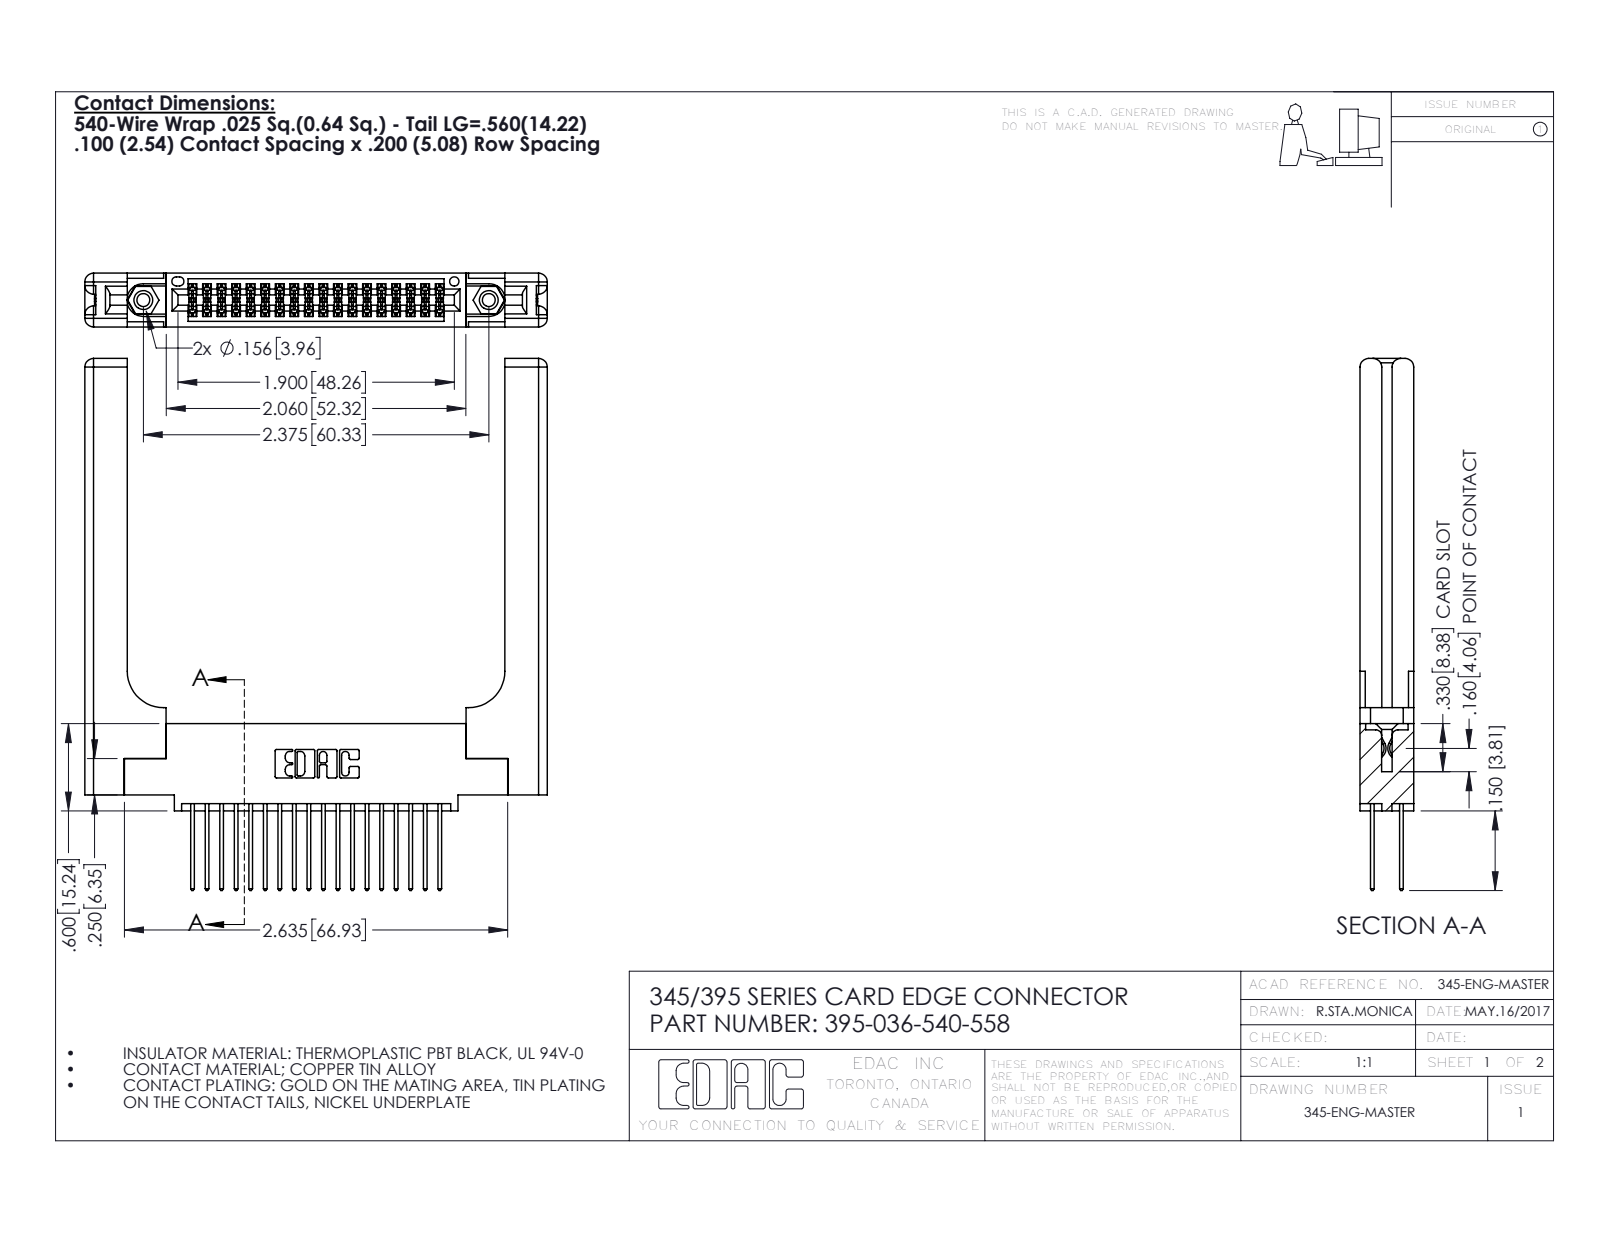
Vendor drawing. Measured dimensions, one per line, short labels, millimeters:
name: 345-250-001_345-250-001-102; 345 Part_0.110 Offset - 0.156 Dia-TH; 345-220-058_345-220-058; 395-036-540-558 (+1 more)
written by: SolidWorks 2016 (CONFIG_CONTROL_DESIGN)
unit: mm
bodies: 41 solids, 2186 faces (1420 planar, 706 cylindrical, 60 other)
size: 92.9 × 80.7 × 9.4
volume: 16 200 mm³; area: 16 680 mm²
holes: 2× ⌀2.3, 2× ⌀3.2, 2× ⌀4, 1× ⌀1.6
bosses: 2× ⌀3.9
rounds: 54× R0.2, 36× R0.3, 22× R0.3, 16× R1.5, 6× R0.2, 6× R0.8, 3× R0.7, 2× R0.4
face distances: 9.4, 1.8, 7.6, 2.5, 6.9, 0.6, 5.1, 3.8, 3.8, 5.7
hole spacings: 6.9, 54.4, 60.3
